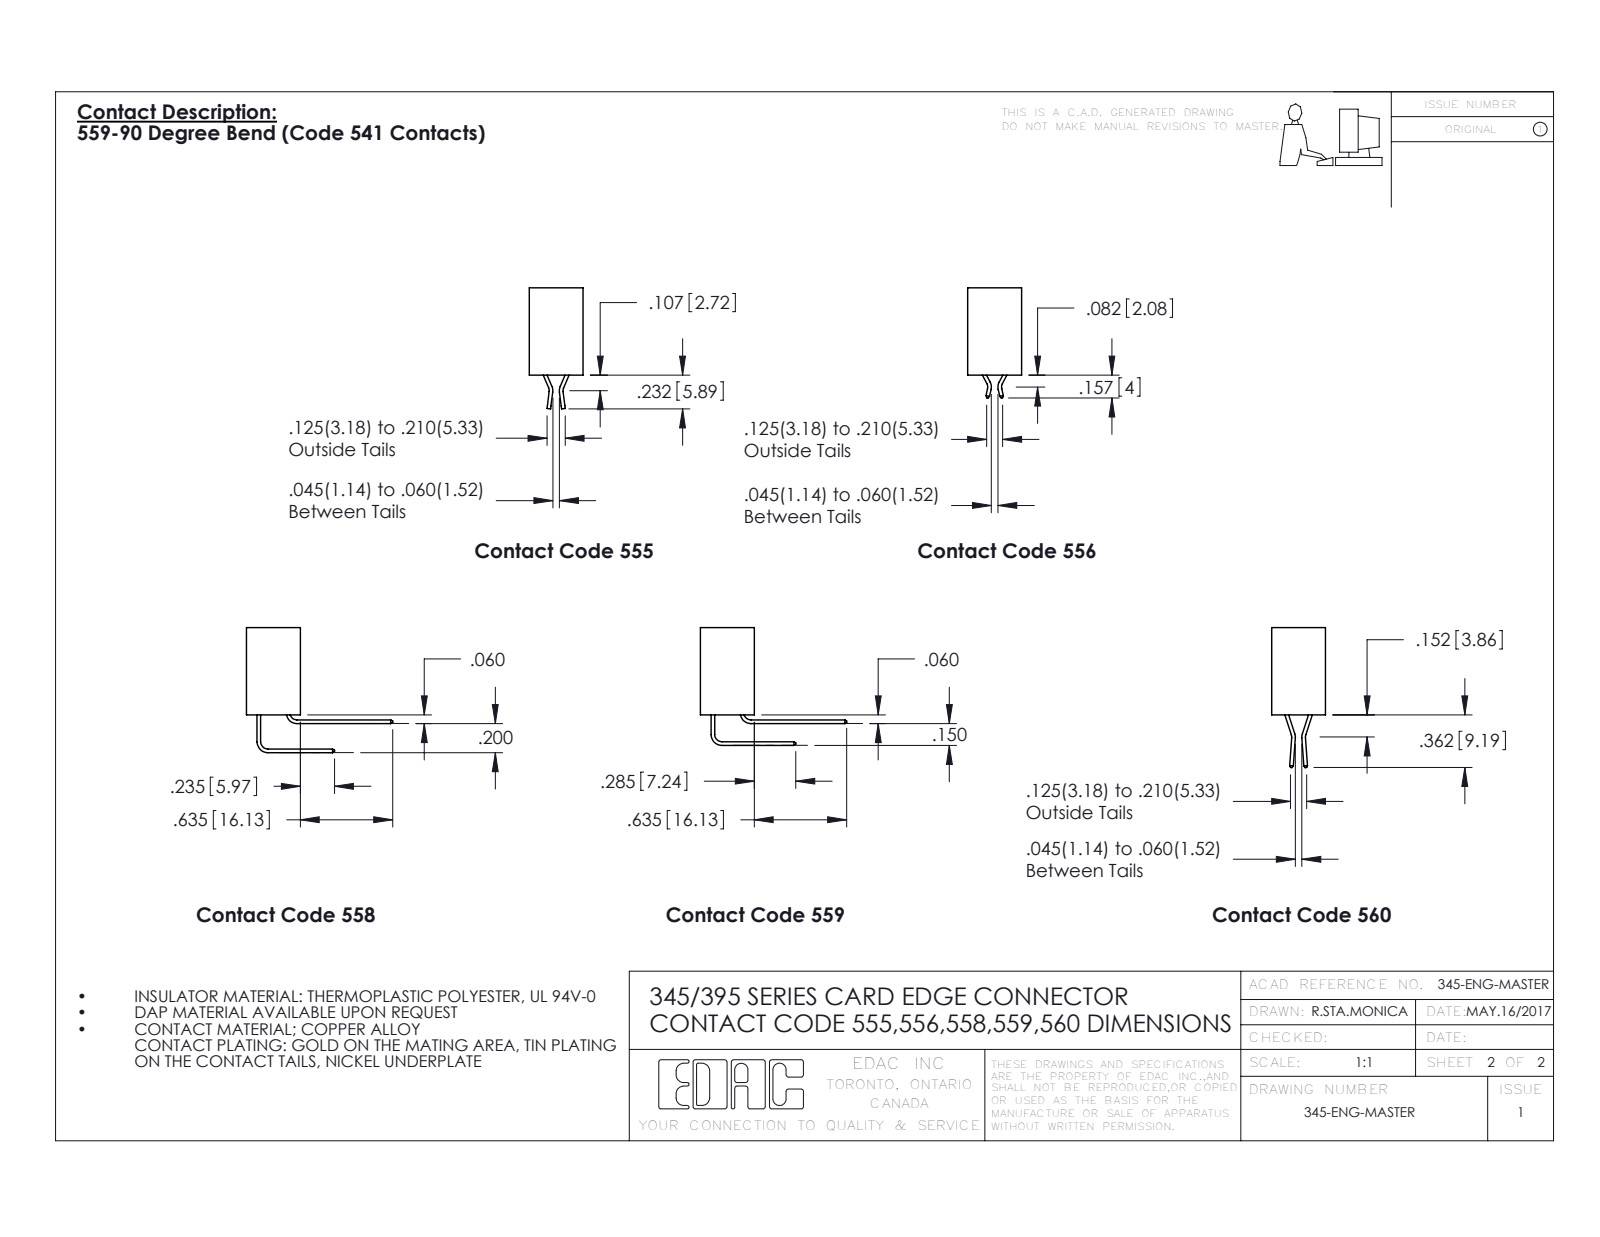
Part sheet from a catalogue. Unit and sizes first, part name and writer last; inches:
Units: inches
Overall size (bounding box): 4.335 × 0.859 × 0.605
Round holes (diameter × count): ⌀0.128 ×2, ⌀0.064 ×1
Partial cylindrical surfaces — rounded edges, fillets, slot ends (radius × count): R0.006 ×70, R0.01 ×22, R0.007 ×6, R0.031 ×6, R0.026 ×3, R0.031 ×2, R0.04 ×2, R0.014 ×1
Main face-to-face distances: 0.072, 0.298, 0.37, 0.2, 0.098, 0.272, 0.025, 0.225, 0.175, 0.149
Hole centre spacings: 4.075
Volume: 0.63 in³ · Surface area: 22.14 in²
Bodies: 36 solids, 2230 faces (1554 planar, 676 cylindrical, 0 other)
Part name (STEP PRODUCT): 395-035-558-612; 345-292-001_558 Tail - 2; 345 Part_0.170 Offset - Side Mount
STEP written by: SolidWorks 2016 (CONFIG_CONTROL_DESIGN)
